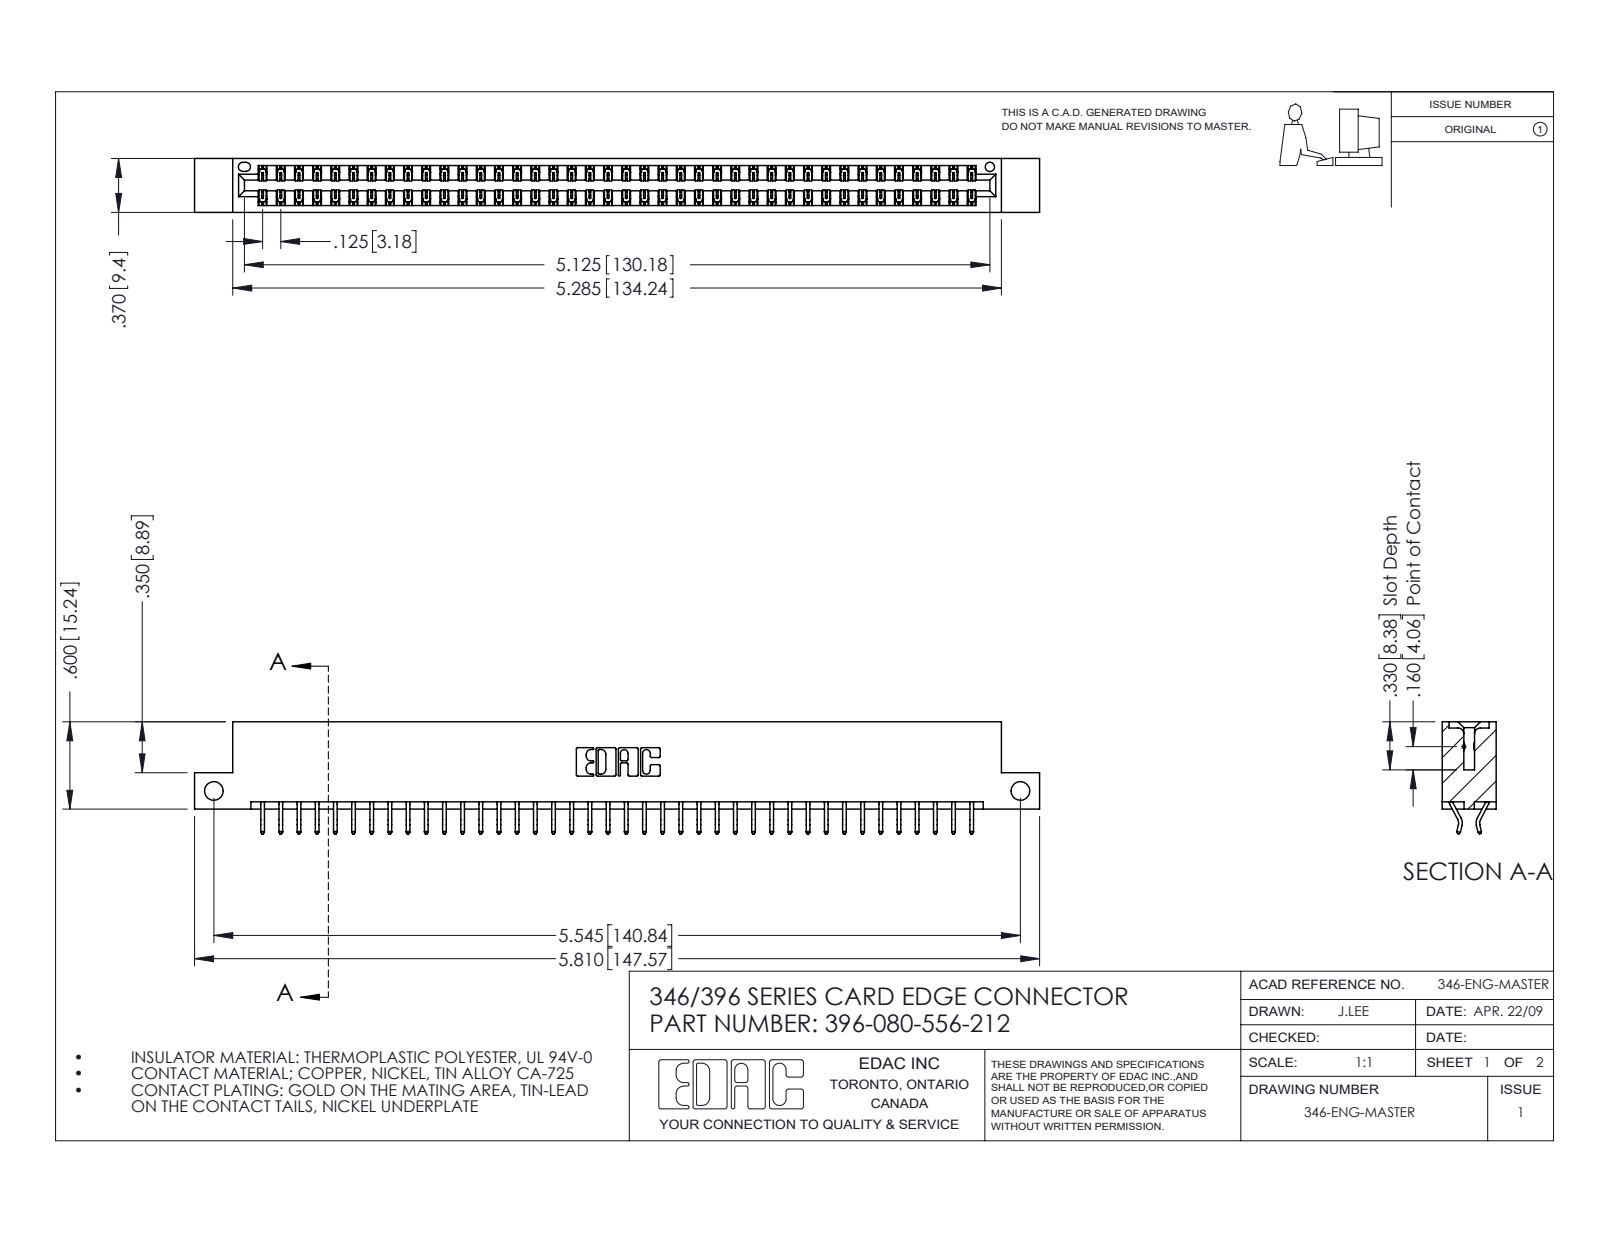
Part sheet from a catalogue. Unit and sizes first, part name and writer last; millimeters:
Units: millimetres
Overall size (bounding box): 147.6 × 19.6 × 9.4
Round holes (diameter × count): ⌀3.3 ×2, ⌀1.6 ×1
Partial cylindrical surfaces — rounded edges, fillets, slot ends (radius × count): R0.2 ×120, R0.3 ×22, R0.2 ×6, R0.8 ×6, R0.7 ×3, R0.3 ×2, R0.4 ×2, R0.6 ×2
Main face-to-face distances: 1.2, 8.2, 9.4, 6.4, 0.6, 1.8, 7.6, 7, 3.8, 5.6
Hole centre spacings: 140.8
Volume: 14 300 mm³ · Surface area: 19 390 mm²
Bodies: 81 solids, 4762 faces (3196 planar, 1566 cylindrical, 0 other)
Part name (STEP PRODUCT): 346 Part_Flush Mounting Lugs - Side Mount; 345-292-001_556 Tail; 396-080-556-212
STEP written by: SolidWorks 2016 (CONFIG_CONTROL_DESIGN)
